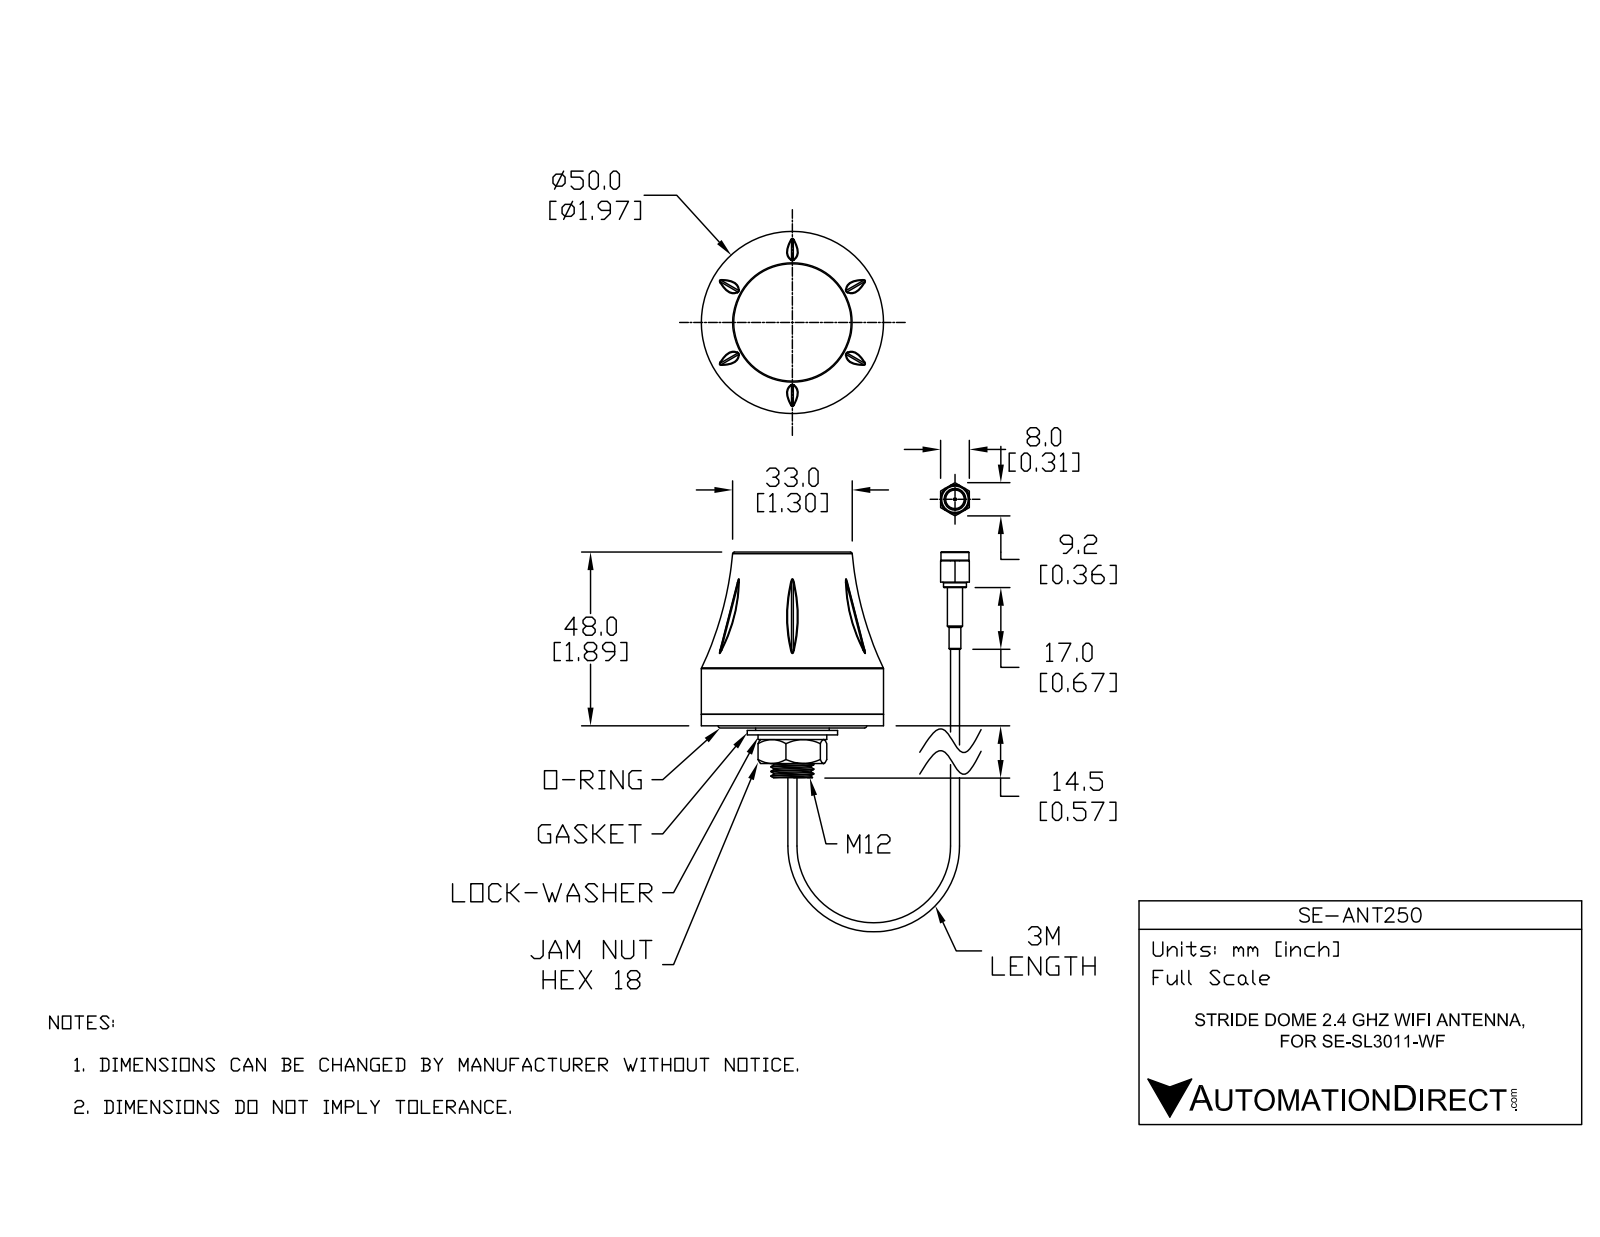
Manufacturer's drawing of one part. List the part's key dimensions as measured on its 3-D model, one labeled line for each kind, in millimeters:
Part name (STEP PRODUCT): SE-ANT150
STEP written by: SolidWorks 2017 (AUTOMOTIVE_DESIGN)
Units: millimetres
Bodies: 2 solids, 112 faces (40 planar, 18 cylindrical, 54 other)
Overall size (bounding box): 105.4 × 74 × 50.3
Volume: 73 460 mm³ · Surface area: 16 450 mm²
Round holes (diameter × count): ⌀5.6 ×1, ⌀6.4 ×1
Round bosses / shafts (diameter × count): ⌀50.3 ×1, ⌀13.3 ×1, ⌀11.8 ×1, ⌀7.7 ×1, ⌀6.4 ×1, ⌀5.1 ×1, ⌀4.2 ×1, ⌀3.3 ×1
Partial cylindrical surfaces — rounded edges, fillets, slot ends (radius × count): R0.5 ×6
Main face-to-face distances: 3.2, 48.5, 45.3, 8, 1.3, 4.4, 49.7, 13.1, 14.4, 17.5
Hole centre spacings: 44.9
